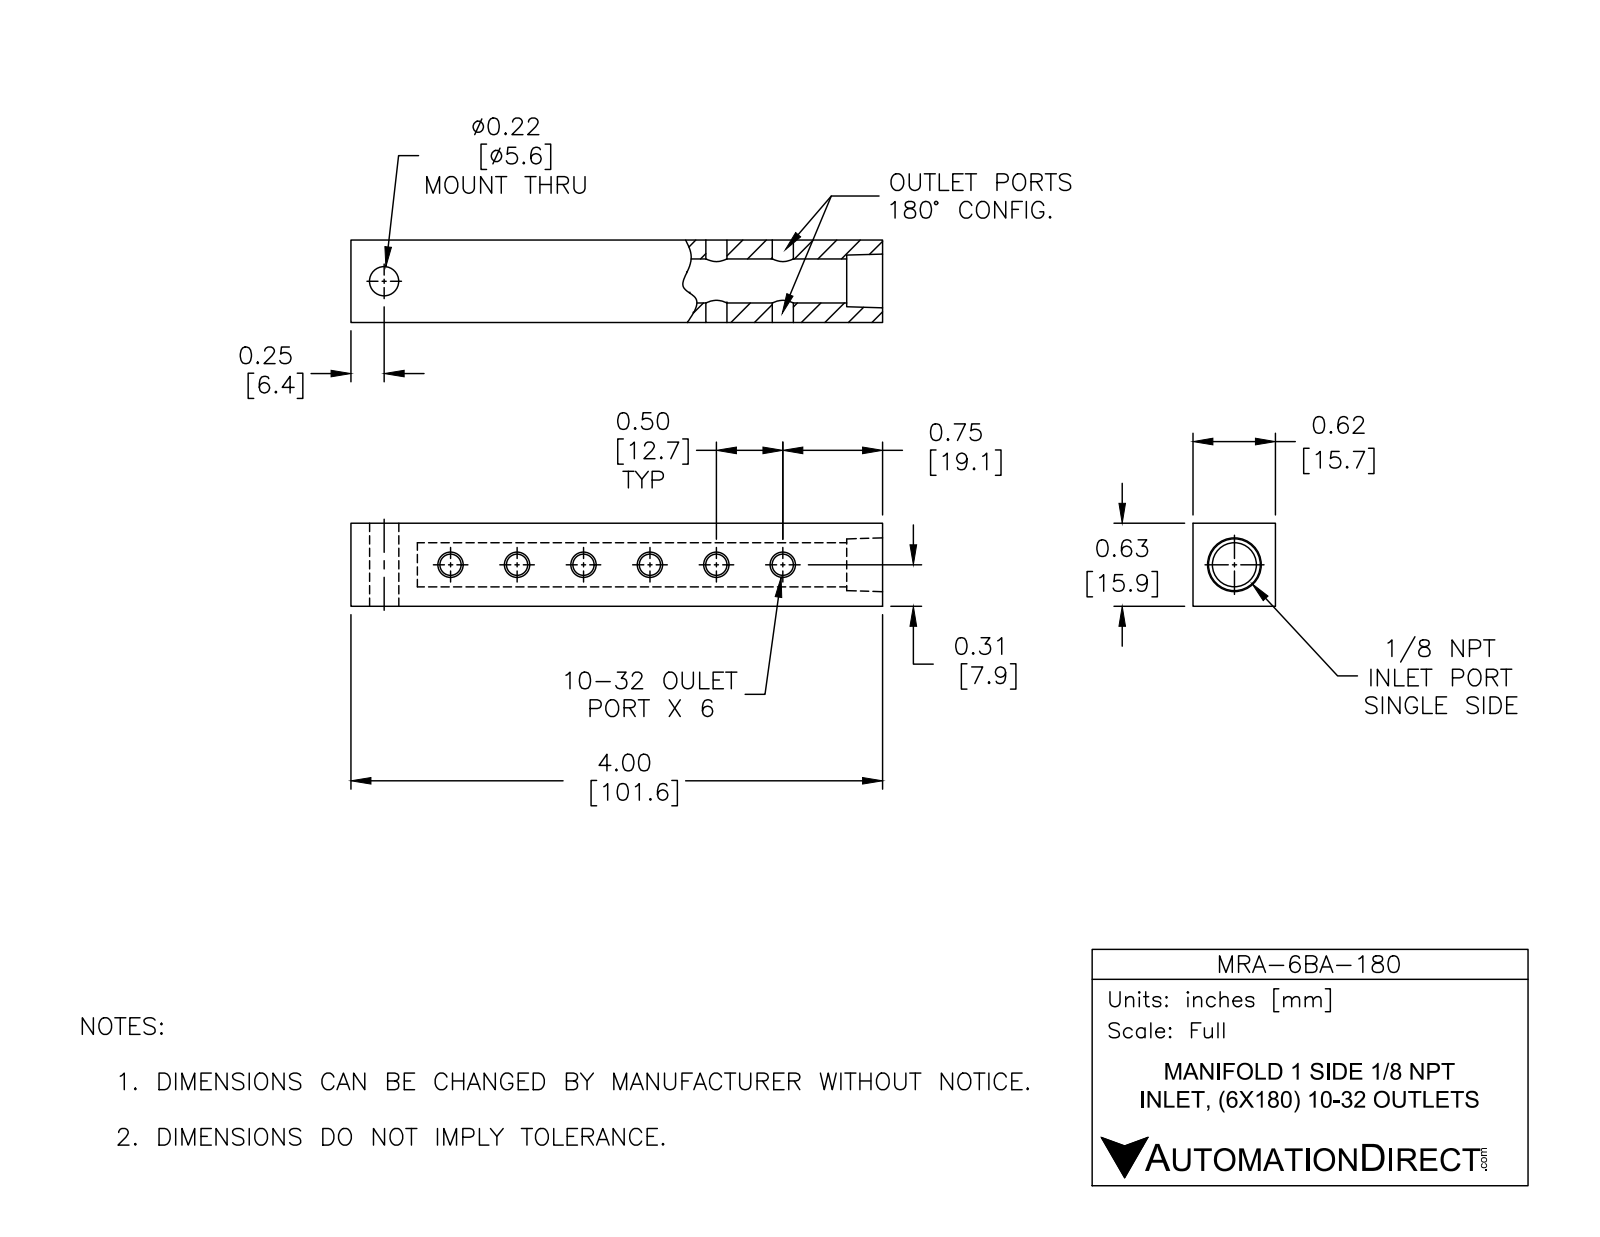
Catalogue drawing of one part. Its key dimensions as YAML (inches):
part_name: "MRA-6BA-180"
step_written_by: "SolidWorks 2015 (CONFIG_CONTROL_DESIGN)"
units: inches
bodies: {solids: 1, faces: 38, planar: 8, cylindrical: 28, other: 2}
overall_size: [4, 0.625, 0.62]
volume: 1.178
surface_area: 15.23
round_holes:
  - {diameter: 0.159, count: 6}
  - {diameter: 0.22, count: 1}
  - {diameter: 0.332, count: 1}
face_to_face_distances: [0.625, 0.62, 4, 0.5, 3.5, 3.73, 3.23, 0.27]
hole_center_spacings: [0.5, 1, 1.5, 2, 2.5]
